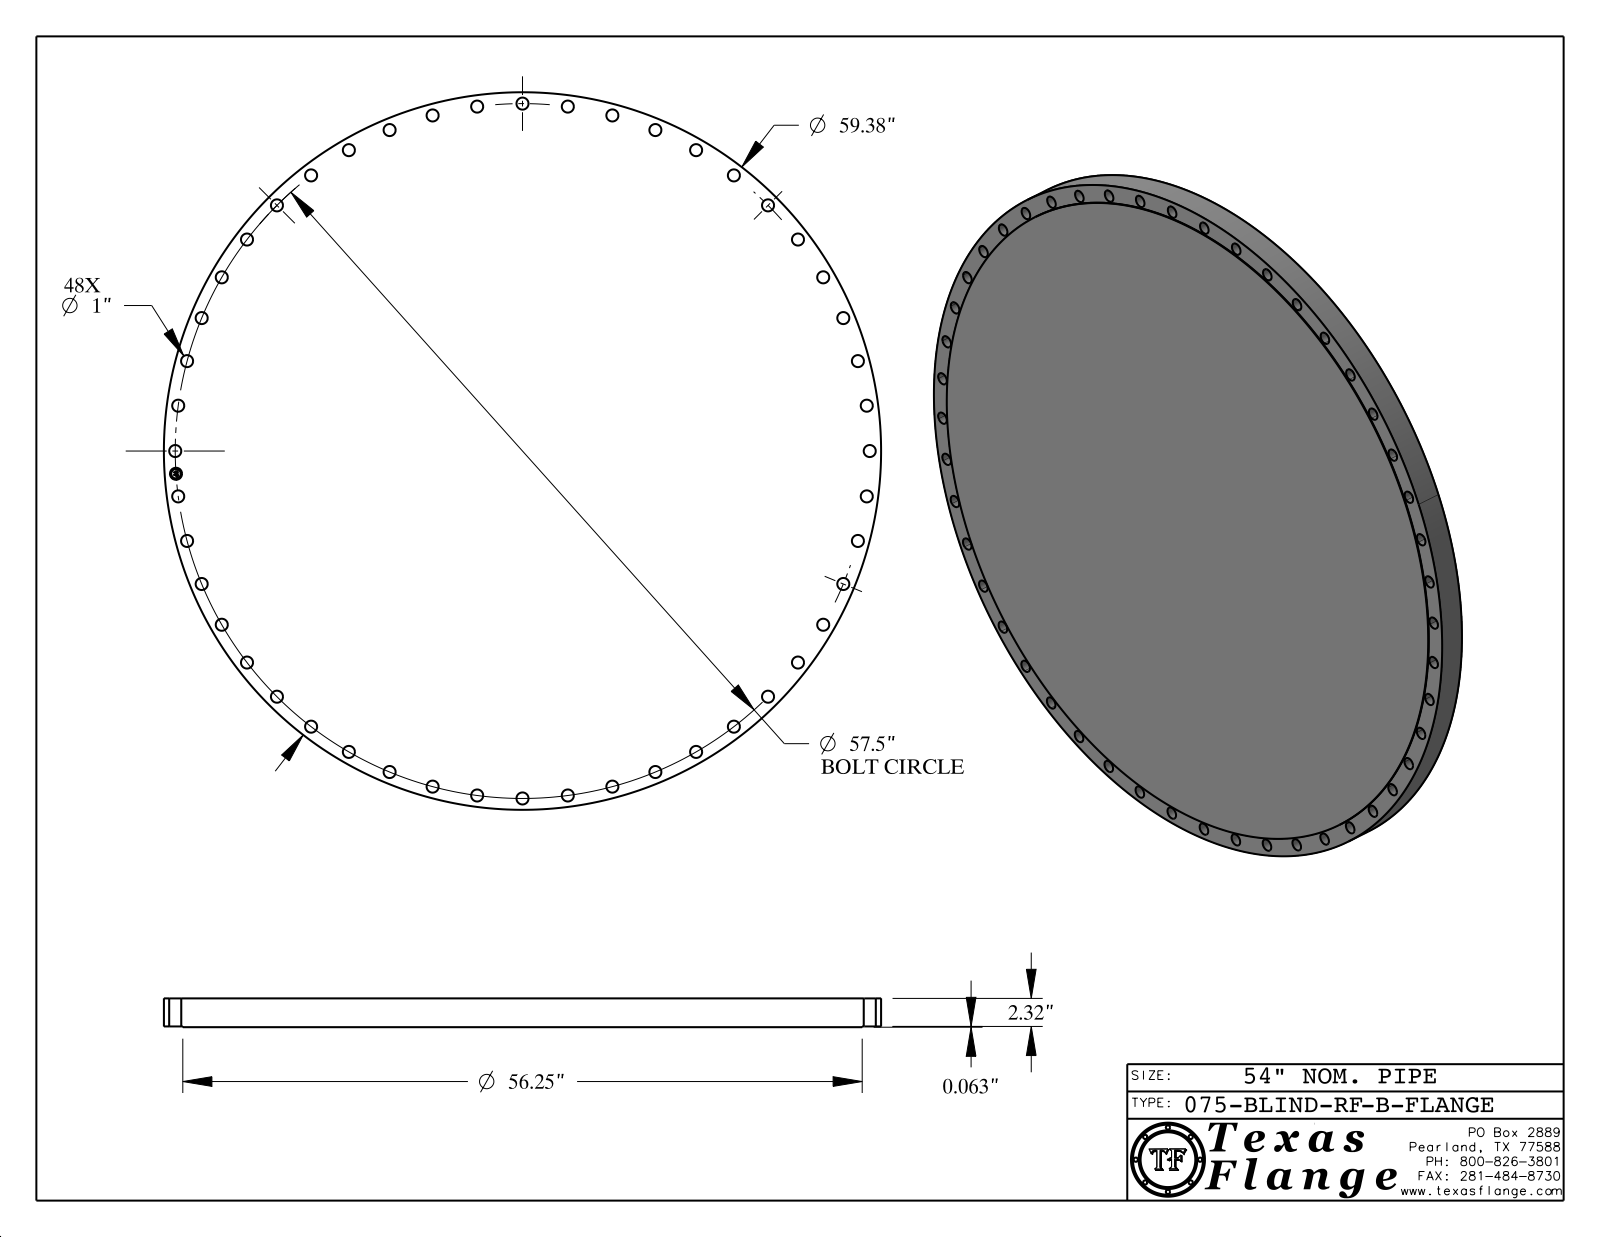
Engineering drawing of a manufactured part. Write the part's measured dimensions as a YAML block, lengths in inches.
part_name: "075-BLIND-RF, Series B"
step_written_by: "CATIA V5 STEP AP214 (AUTOMOTIVE_DESIGN)"
units: inches
bodies: {solids: 1, faces: 488, planar: 368, cylindrical: 120, other: 0}
overall_size: [59.38, 59.38, 2.383]
volume: 6494
surface_area: 6257
round_holes:
  - {diameter: 1, count: 49}
round_bosses_or_shafts:
  - {diameter: 0.061, count: 8}
  - {diameter: 59.38, count: 1}
  - {diameter: 56.25, count: 1}
  - {diameter: 0.788, count: 1}
face_to_face_distances: [2.383, 0.063, 2.32, 0.015, 2.368, 2.305, 0.298, 0.293, 0.054, 0.193]
hole_center_spacings: [11.218, 57.377, 3.761, 22.004, 57.008, 7.505, 18.483, 14.882]
